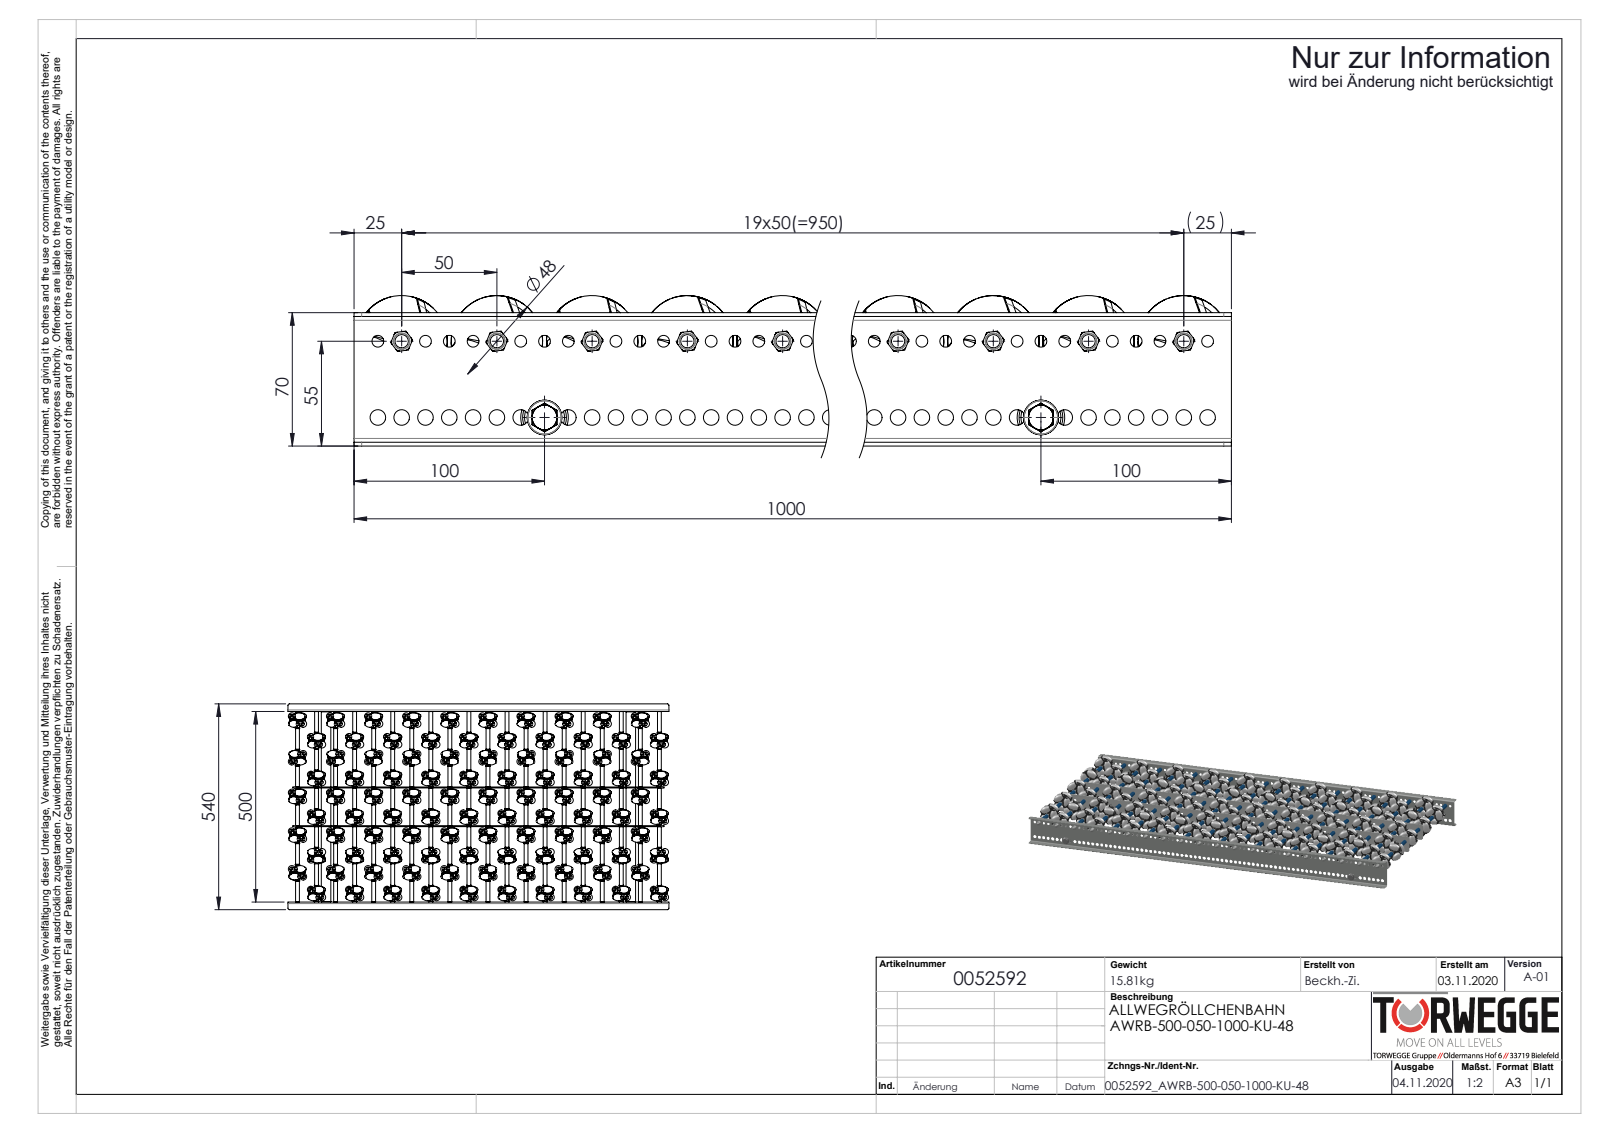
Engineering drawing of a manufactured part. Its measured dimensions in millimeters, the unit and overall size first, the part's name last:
Units: millimetres
Overall size (bounding box): 1000 × 540 × 78.99
Round holes (diameter × count): ⌀3.7 ×600, ⌀4.2 ×600, ⌀6.2 ×79, ⌀8.2 ×79, ⌀6.5 ×39, ⌀4.92 ×20, ⌀8.4 ×20, ⌀6.8 ×2, ⌀21 ×2
Round bosses / shafts (diameter × count): ⌀4 ×600, ⌀3.7 ×529, ⌀8 ×22, ⌀42 ×20, ⌀11 ×20, ⌀10 ×20, ⌀7 ×20, ⌀6 ×20
Partial cylindrical surfaces — rounded edges, fillets, slot ends (radius × count): R23.55 ×20, R4 ×8, R2 ×4, R5 ×4
Main face-to-face distances: 2, 502, 101.5, 2.5, 68, 500, 504, 99, 301.4, 104
Hole centre spacings: 36.06, 36.05, 100, 50, 36.07, 200, 36.04, 30.99
Volume: 5 560 000 mm³ · Surface area: 3 764 000 mm²
Bodies: 1674 solids, 29608 faces (10292 planar, 11452 cylindrical, 7864 other)
Part name (STEP PRODUCT): 0036819_SICHERUNGS-HUTMUTTER-DIN986-M6; Traversen_KFG_L500; 0019719_Gewindestange-M6_L=520; 0052592 (+8 more)
STEP written by: SolidWorks 2020 (AUTOMOTIVE_DESIGN)
